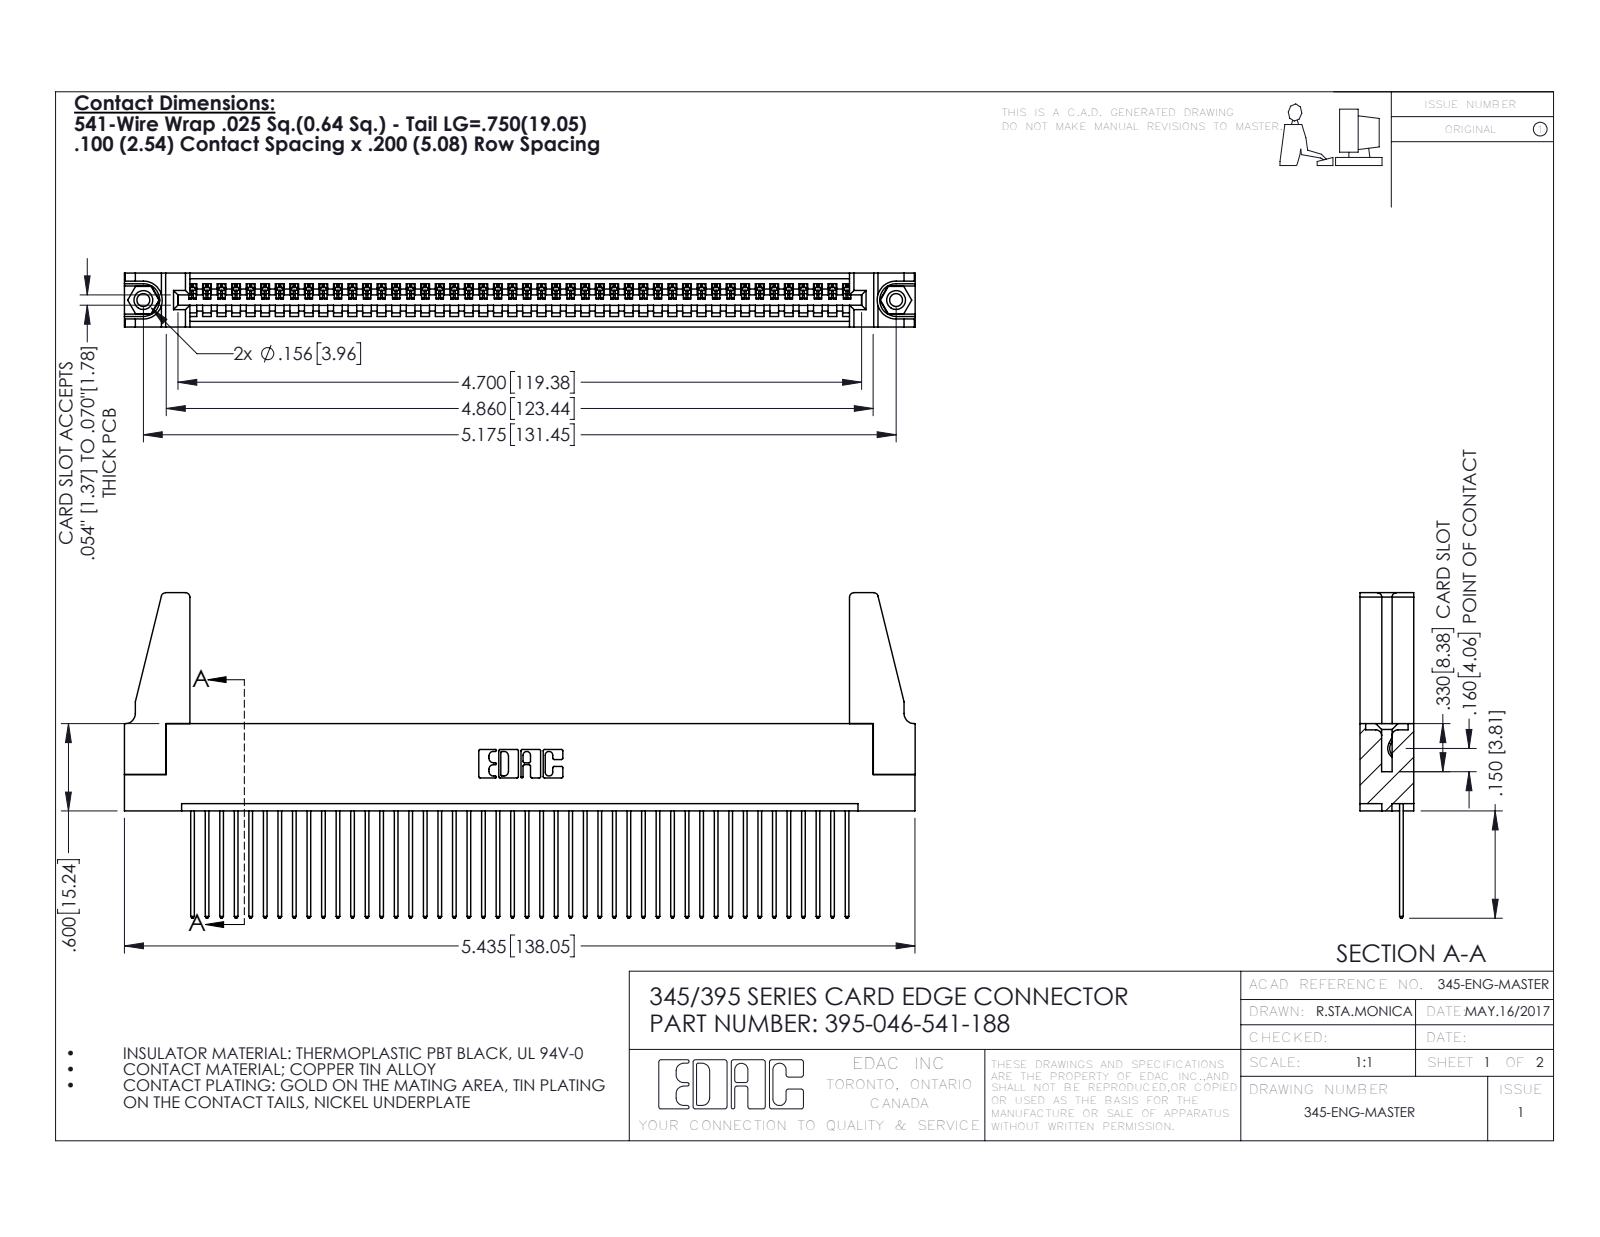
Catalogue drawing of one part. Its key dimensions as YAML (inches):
part_name: "345-220-078_345-220-088; 345-292-001_345-293-141; 345 Part_Flush Mounting Lugs - 0.156 Dia-TH; 345-250-001_345-250-001-102 (+1 more)"
step_written_by: "SolidWorks 2016 (CONFIG_CONTROL_DESIGN)"
units: inches
bodies: {solids: 51, faces: 2918, planar: 1992, cylindrical: 910, other: 16}
overall_size: [5.436, 2.237, 0.37]
volume: 1.01
surface_area: 33.71
round_holes:
  - {diameter: 0.089, count: 2}
  - {diameter: 0.125, count: 2}
  - {diameter: 0.156, count: 2}
  - {diameter: 0.064, count: 1}
round_bosses_or_shafts:
  - {diameter: 0.155, count: 2}
partial_cylinders:
  - {radius: 0.006, count: 92}
  - {radius: 0.01, count: 92}
  - {radius: 0.01, count: 22}
  - {radius: 0.03, count: 8}
  - {radius: 0.007, count: 6}
  - {radius: 0.031, count: 6}
  - {radius: 0.026, count: 3}
  - {radius: 0.031, count: 2}
face_to_face_distances: [0.072, 0.298, 0.37, 0.098, 0.272, 0.025, 0.2, 0.225, 0.149, 0.072]
hole_center_spacings: [0.27, 4.939, 5.175]
